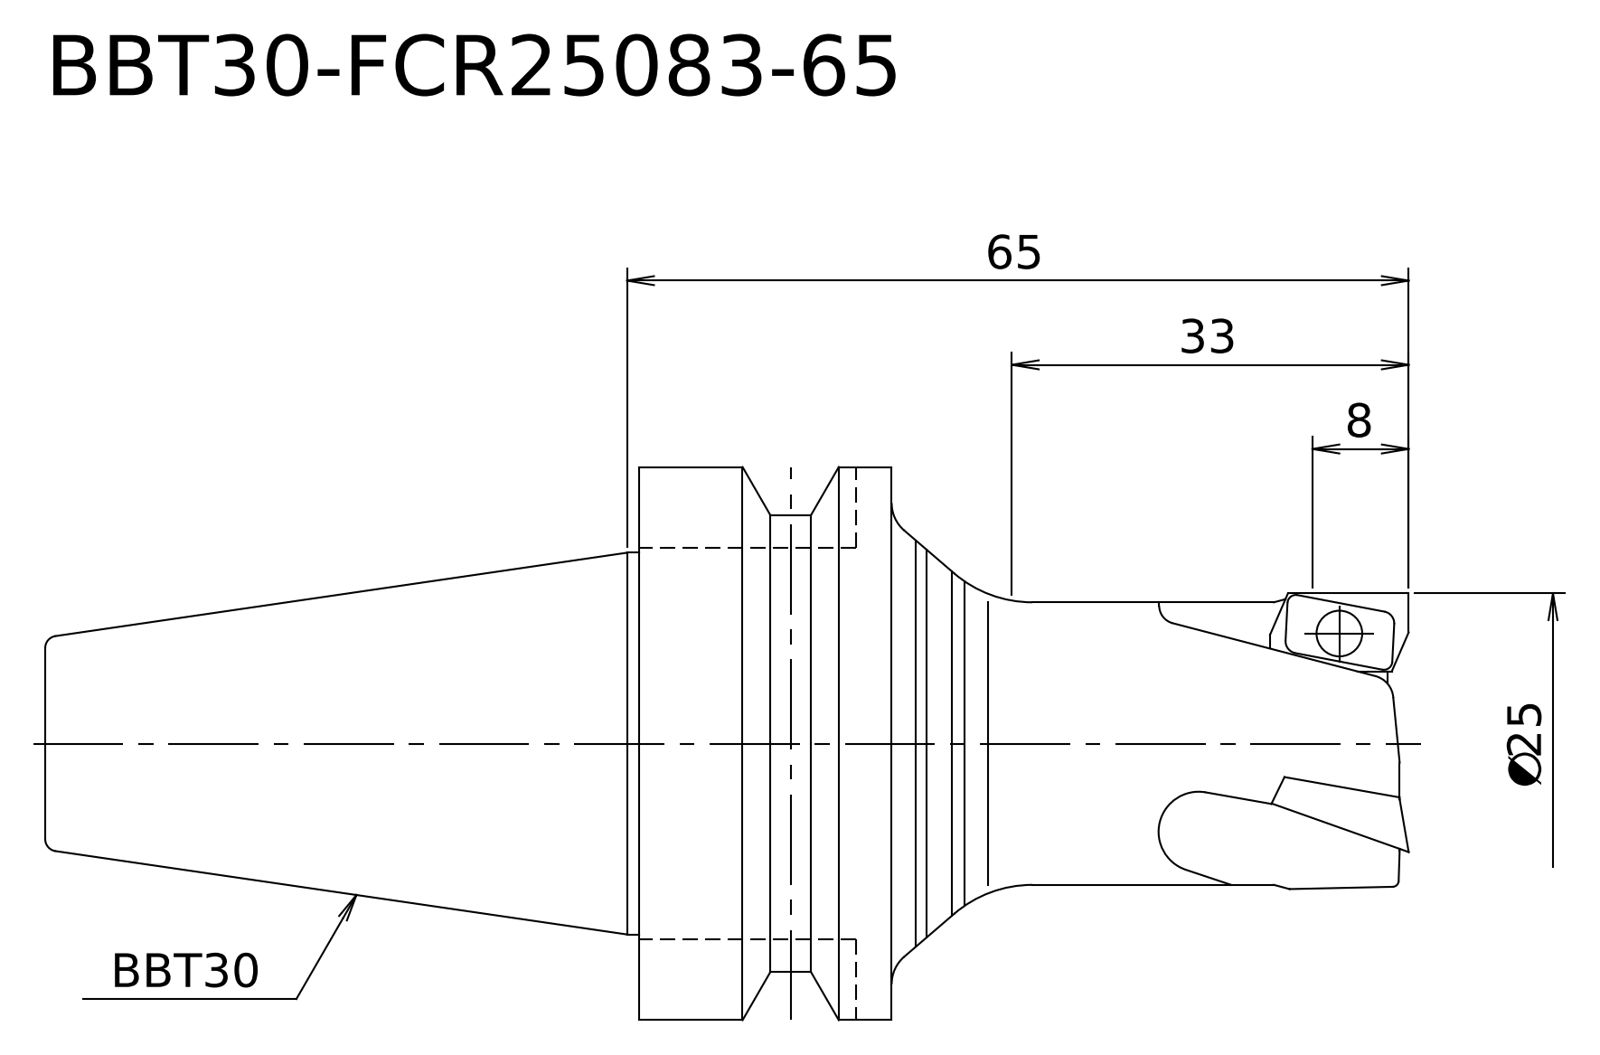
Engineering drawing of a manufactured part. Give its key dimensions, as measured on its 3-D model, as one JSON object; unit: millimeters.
{"step_written_by": "Kubotek KeyCreator V8.5.1 (14335) (CONFIG_CONTROL_DESIGN)", "units": "millimeters", "bodies": {"solids": 1, "faces": 17, "planar": 4, "cylindrical": 6, "other": 7}, "overall_size": [113.4, 46, 46], "volume_mm3": 78515, "surface_area_mm2": 13178, "round_bosses_or_shafts": [[46, 1], [38, 1], [31.75, 1], [25, 1], [23.5, 1]], "face_to_face_distances": [64, 43, 21, 113.4, 70.4, 49.4]}
